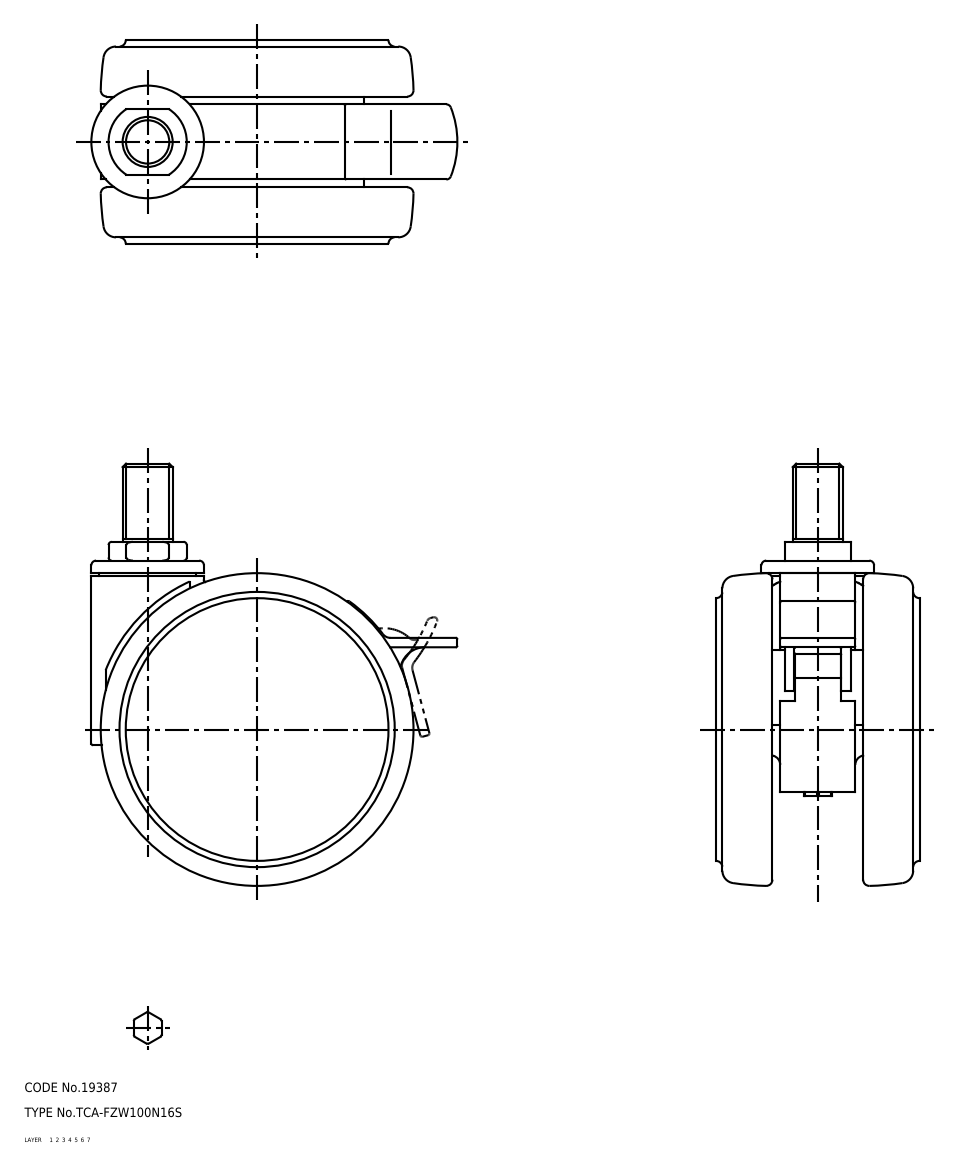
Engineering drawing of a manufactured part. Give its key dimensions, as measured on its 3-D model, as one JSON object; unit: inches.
{"part_name": "caster; TCA-FZW100N16S", "step_written_by": "SolidWorks 2015 (AUTOMOTIVE_DESIGN)", "units": "inches", "bodies": {"solids": 1, "faces": 2495, "planar": 865, "cylindrical": 1191, "other": 439}, "overall_size": [5.315, 4.607, 2.567], "volume_in3": 18.7, "surface_area_in2": 194.3, "round_holes": [[0.11, 1], [0.118, 1], [0.13, 1], [0.161, 1], [0.165, 1], [0.236, 1], [0.358, 1], [0.394, 1], [0.398, 1], [0.413, 1], [0.433, 1], [0.472, 1]], "round_bosses_or_shafts": [[3.457, 1], [1.417, 1], [1.22, 1], [1.098, 1], [1.087, 1], [0.787, 1], [0.748, 1], [0.709, 1]], "partial_cylinders_radius": [[0.02, 236], [0.047, 160], [0.039, 87], [0.079, 25], [0.059, 23], [0.008, 18], [0.012, 12], [0.118, 8]], "face_to_face_distances": [0.071, 2.425, 2.496, 0.142, 2.354, 0.571, 0.642, 1.783, 0.713, 1.854], "hole_center_spacings": [0.897, 1.159, 1.732]}
